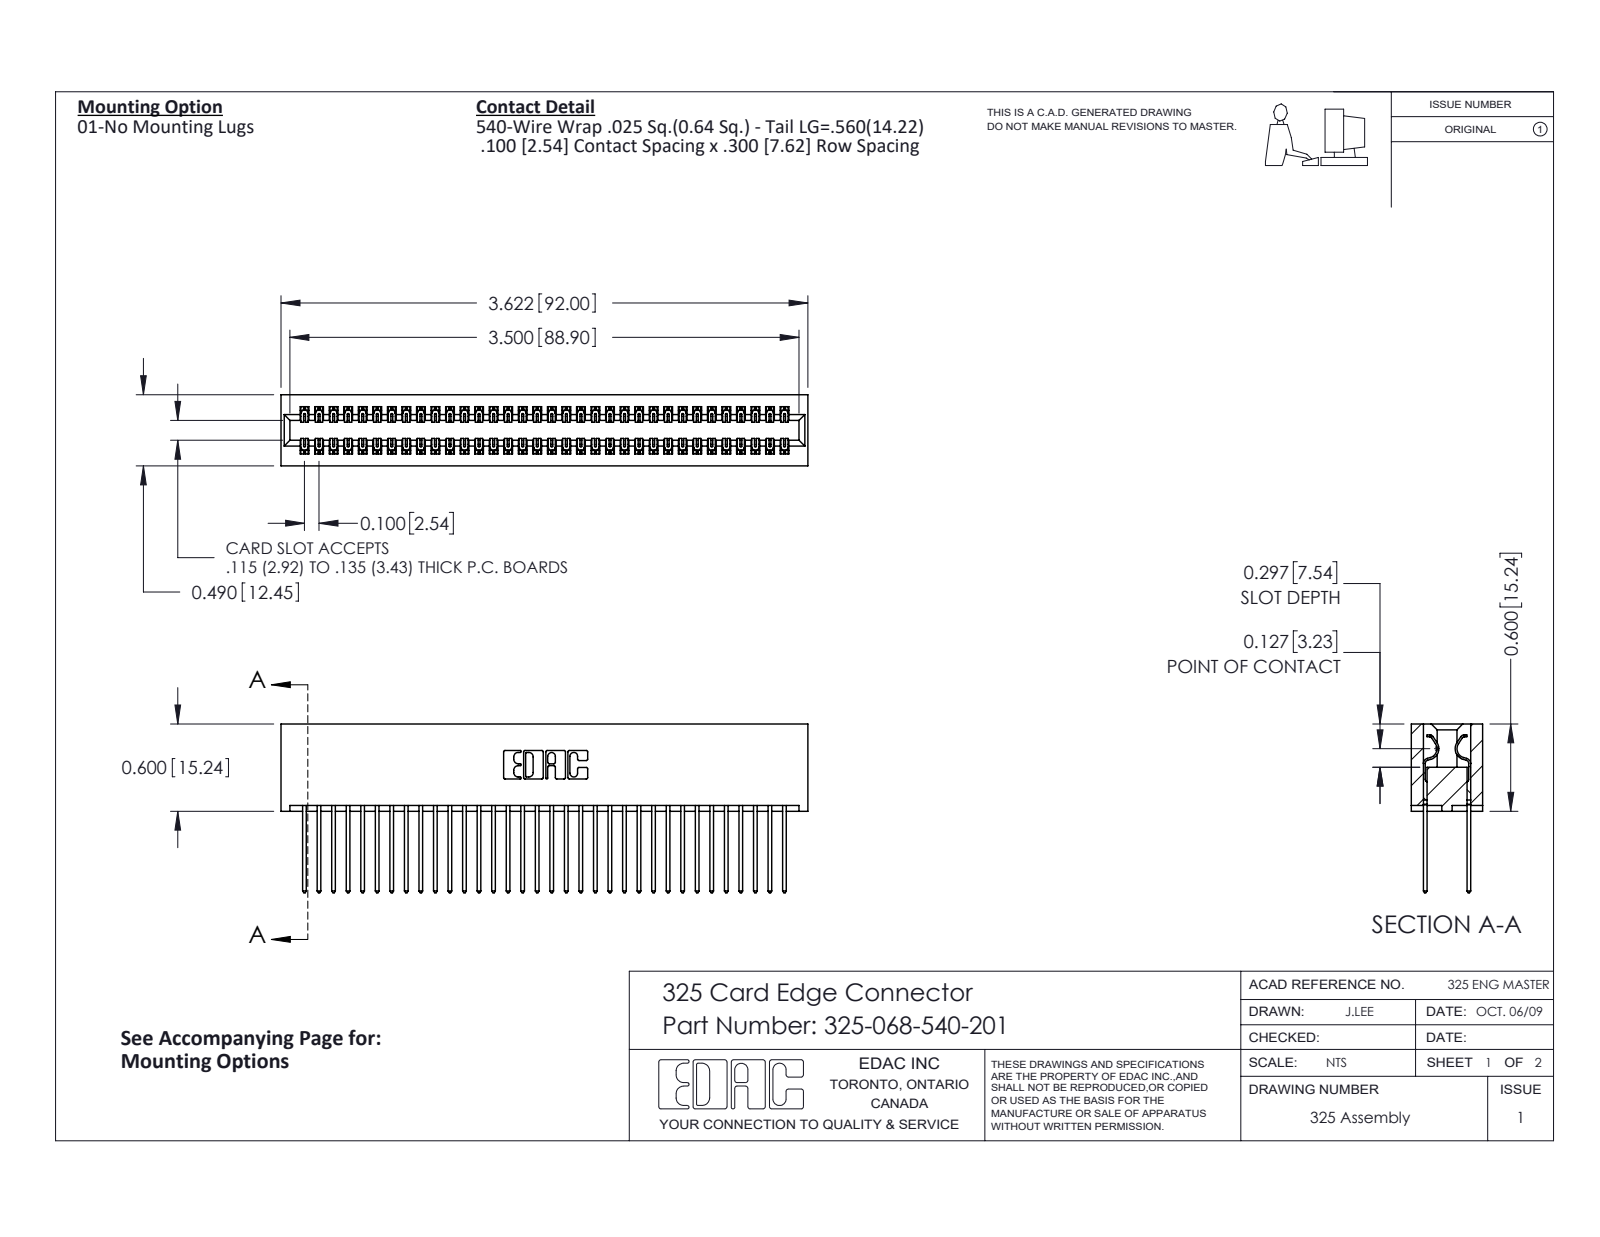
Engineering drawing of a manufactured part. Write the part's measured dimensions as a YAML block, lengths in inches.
part_name: "325-292-001_325-293-140; 325 Part_Lugless; 325-068-540-201"
step_written_by: "SolidWorks 2016 (CONFIG_CONTROL_DESIGN)"
units: inches
bodies: {solids: 69, faces: 3642, planar: 2514, cylindrical: 1128, other: 0}
overall_size: [3.622, 1.16, 0.49]
volume: 0.773
surface_area: 26.4
partial_cylinders:
  - {radius: 0.006, count: 102}
  - {radius: 0.01, count: 68}
  - {radius: 0.01, count: 22}
  - {radius: 0.007, count: 6}
  - {radius: 0.031, count: 6}
  - {radius: 0.026, count: 3}
  - {radius: 0.014, count: 2}
  - {radius: 0.022, count: 2}
face_to_face_distances: [0.083, 0.407, 0.3, 0.107, 0.383, 0.025, 0.325, 0.49, 0.275, 0.1]
